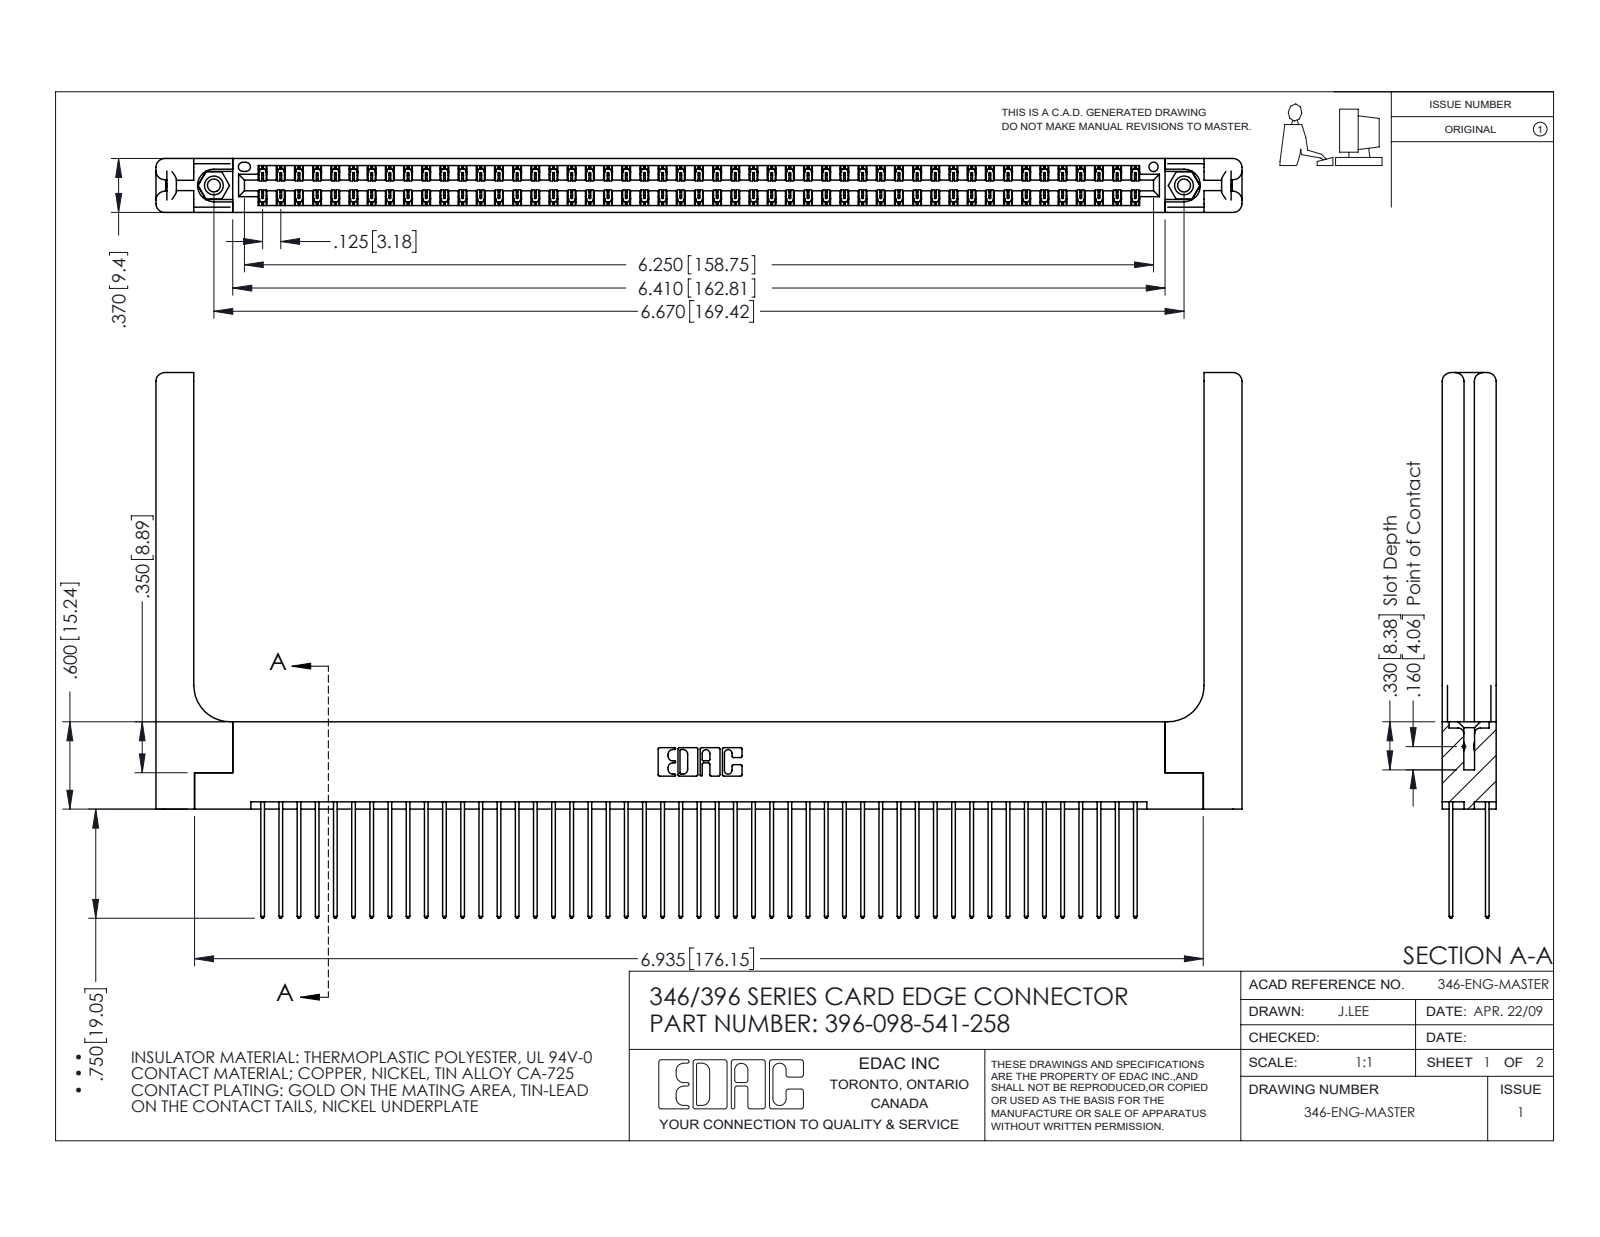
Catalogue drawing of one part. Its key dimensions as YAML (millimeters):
part_name: "345-250-001_345-250-001-102; 345-292-001_345-293-141; 396-098-541-258; 346 Part_Flush Mounting Lugs - 0.156 Dia-TH (+1 more)"
step_written_by: "SolidWorks 2016 (CONFIG_CONTROL_DESIGN)"
units: millimeters
bodies: {solids: 103, faces: 5474, planar: 3654, cylindrical: 1760, other: 60}
overall_size: [189.6, 95.3, 9.4]
volume: 26600
surface_area: 34050
round_holes:
  - {diameter: 2.3, count: 2}
  - {diameter: 3.2, count: 2}
  - {diameter: 4, count: 2}
  - {diameter: 1.6, count: 1}
round_bosses_or_shafts:
  - {diameter: 3.9, count: 2}
partial_cylinders:
  - {radius: 0.2, count: 147}
  - {radius: 0.3, count: 98}
  - {radius: 0.3, count: 22}
  - {radius: 1.5, count: 16}
  - {radius: 0.2, count: 6}
  - {radius: 0.8, count: 6}
  - {radius: 0.7, count: 3}
  - {radius: 0.4, count: 2}
face_to_face_distances: [1.2, 8.2, 1.8, 9.4, 6.4, 0.6, 7.6, 7, 3.8, 3.8]
hole_center_spacings: [6.2, 164.1, 169.4]
